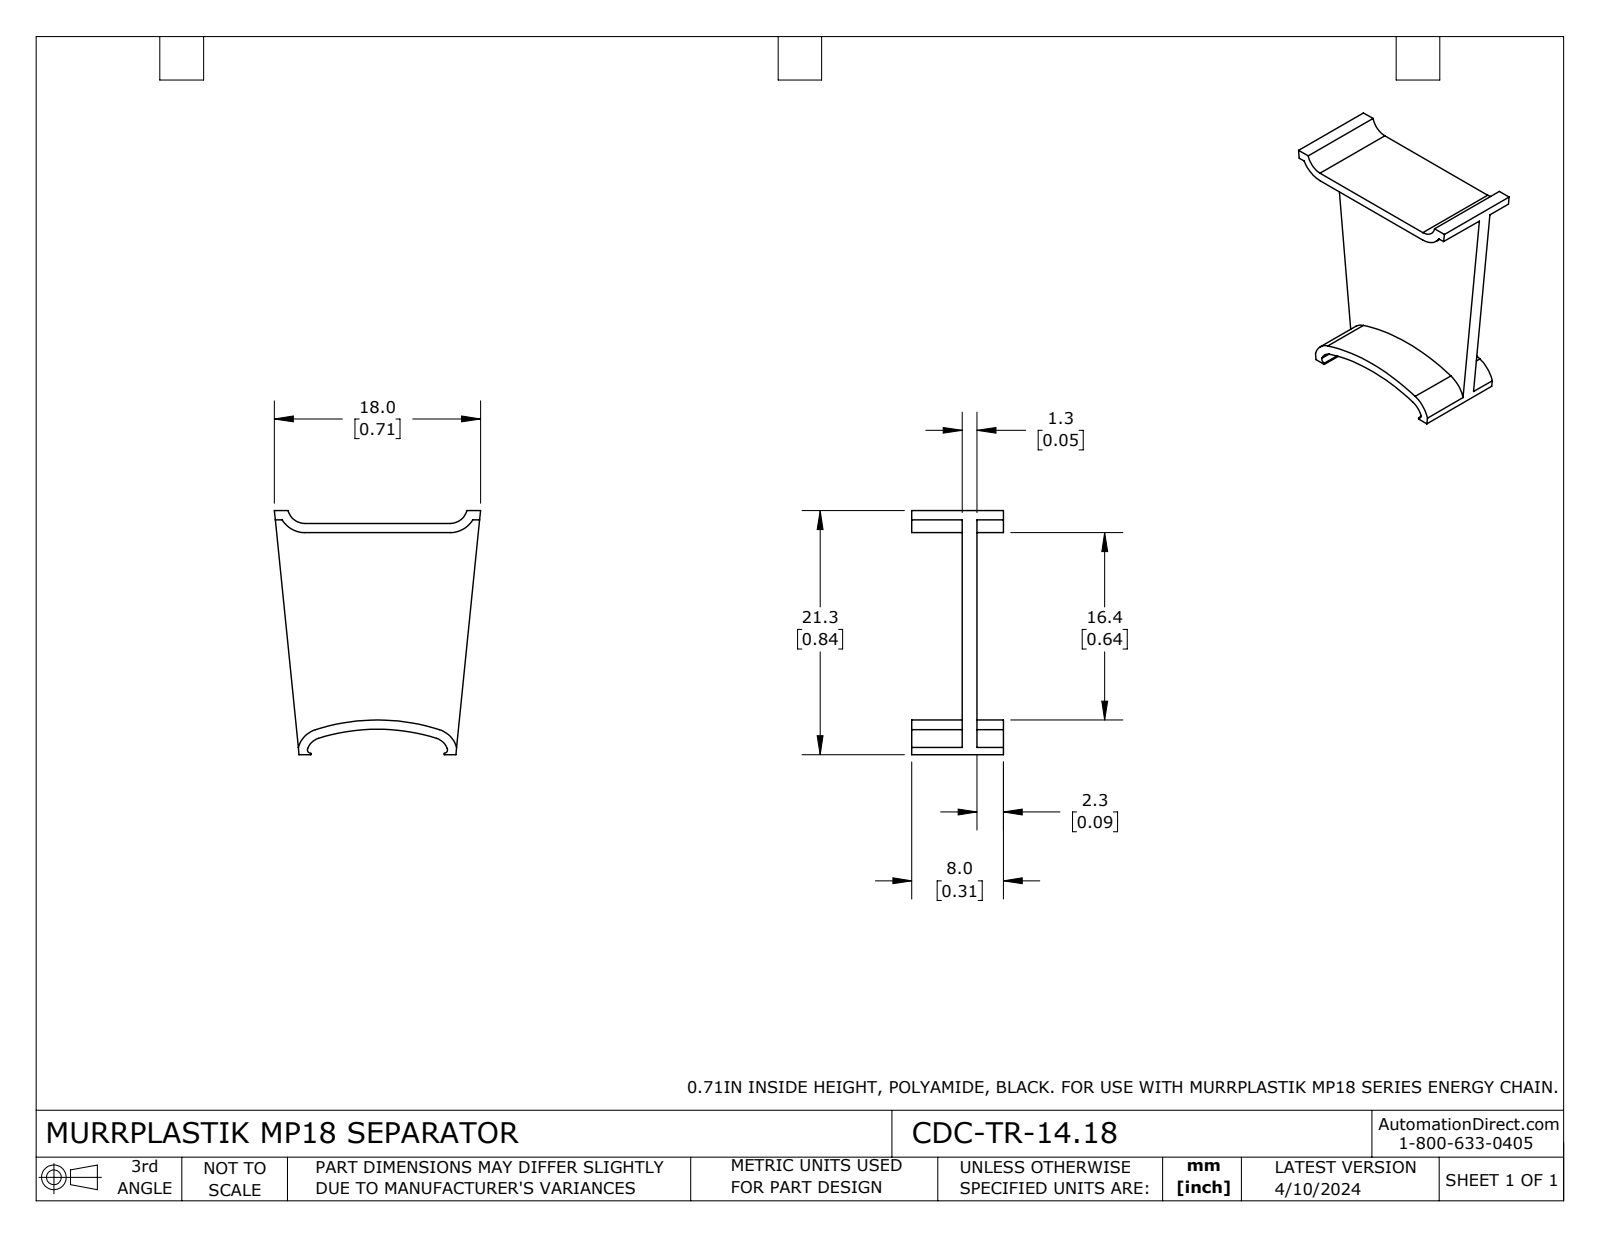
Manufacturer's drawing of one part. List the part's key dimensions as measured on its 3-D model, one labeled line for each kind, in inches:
Part name (STEP PRODUCT): CDC-TR-14.18
STEP written by: SolidWorks 2023 (CONFIG_CONTROL_DESIGN)
Units: inches
Bodies: 1 solid, 39 faces (21 planar, 18 cylindrical, 0 other)
Overall size (bounding box): 0.839 × 0.709 × 0.315
Volume: 0.035 in³ · Surface area: 1.84 in²
Partial cylindrical surfaces — rounded edges, fillets, slot ends (radius × count): R0.059 ×4, R0.091 ×4, R0.012 ×2, R0.669 ×1, R0.701 ×1
Main face-to-face distances: 0.051, 0.031, 0.224, 0.173, 0.091, 0.142, 0.315, 0.044, 0.076, 0.763
